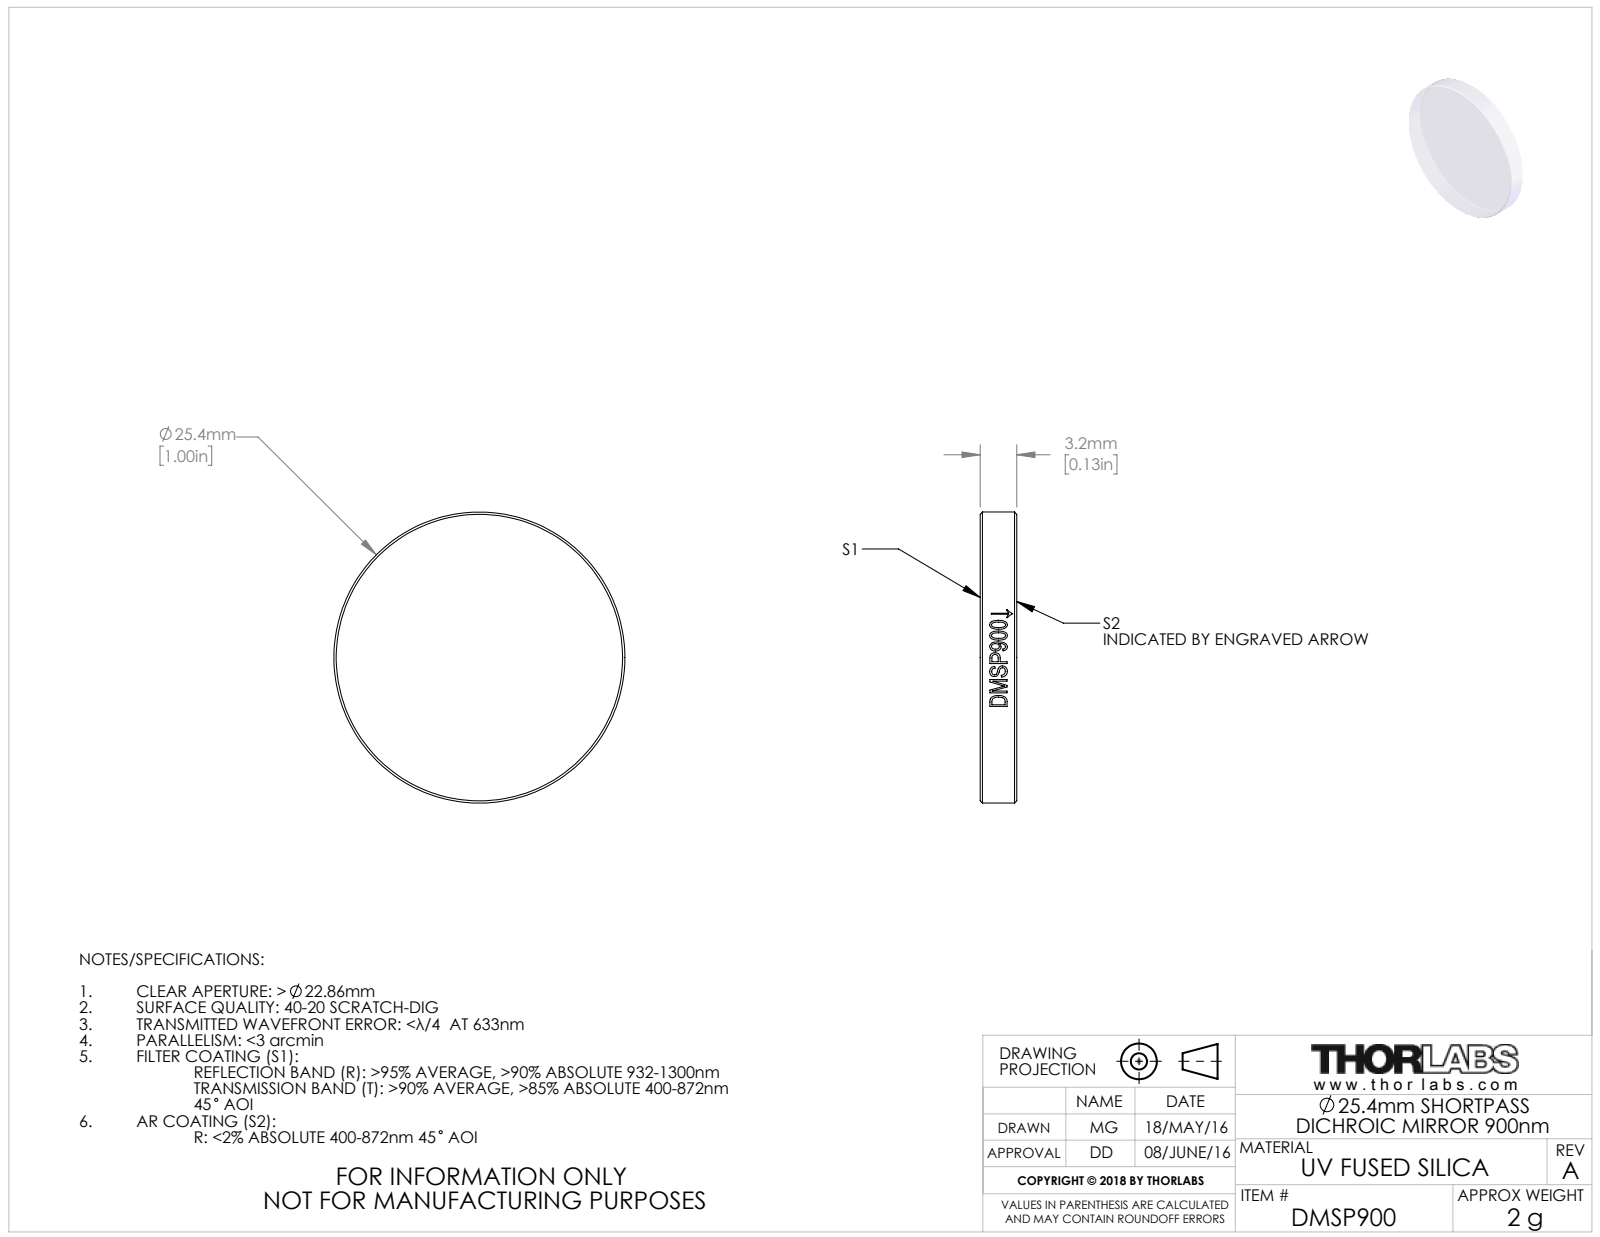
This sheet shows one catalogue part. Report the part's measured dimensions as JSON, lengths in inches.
{"part_name": "TTN045158-E0W", "step_written_by": "SolidWorks 2016 (CONFIG_CONTROL_DESIGN)", "units": "inches", "bodies": {"solids": 1, "faces": 21, "planar": 2, "cylindrical": 15, "other": 4}, "overall_size": [1, 1, 0.126], "volume_in3": 0.099, "surface_area_in2": 1.938, "round_bosses_or_shafts": [[1, 1]], "face_to_face_distances": [0.126]}
